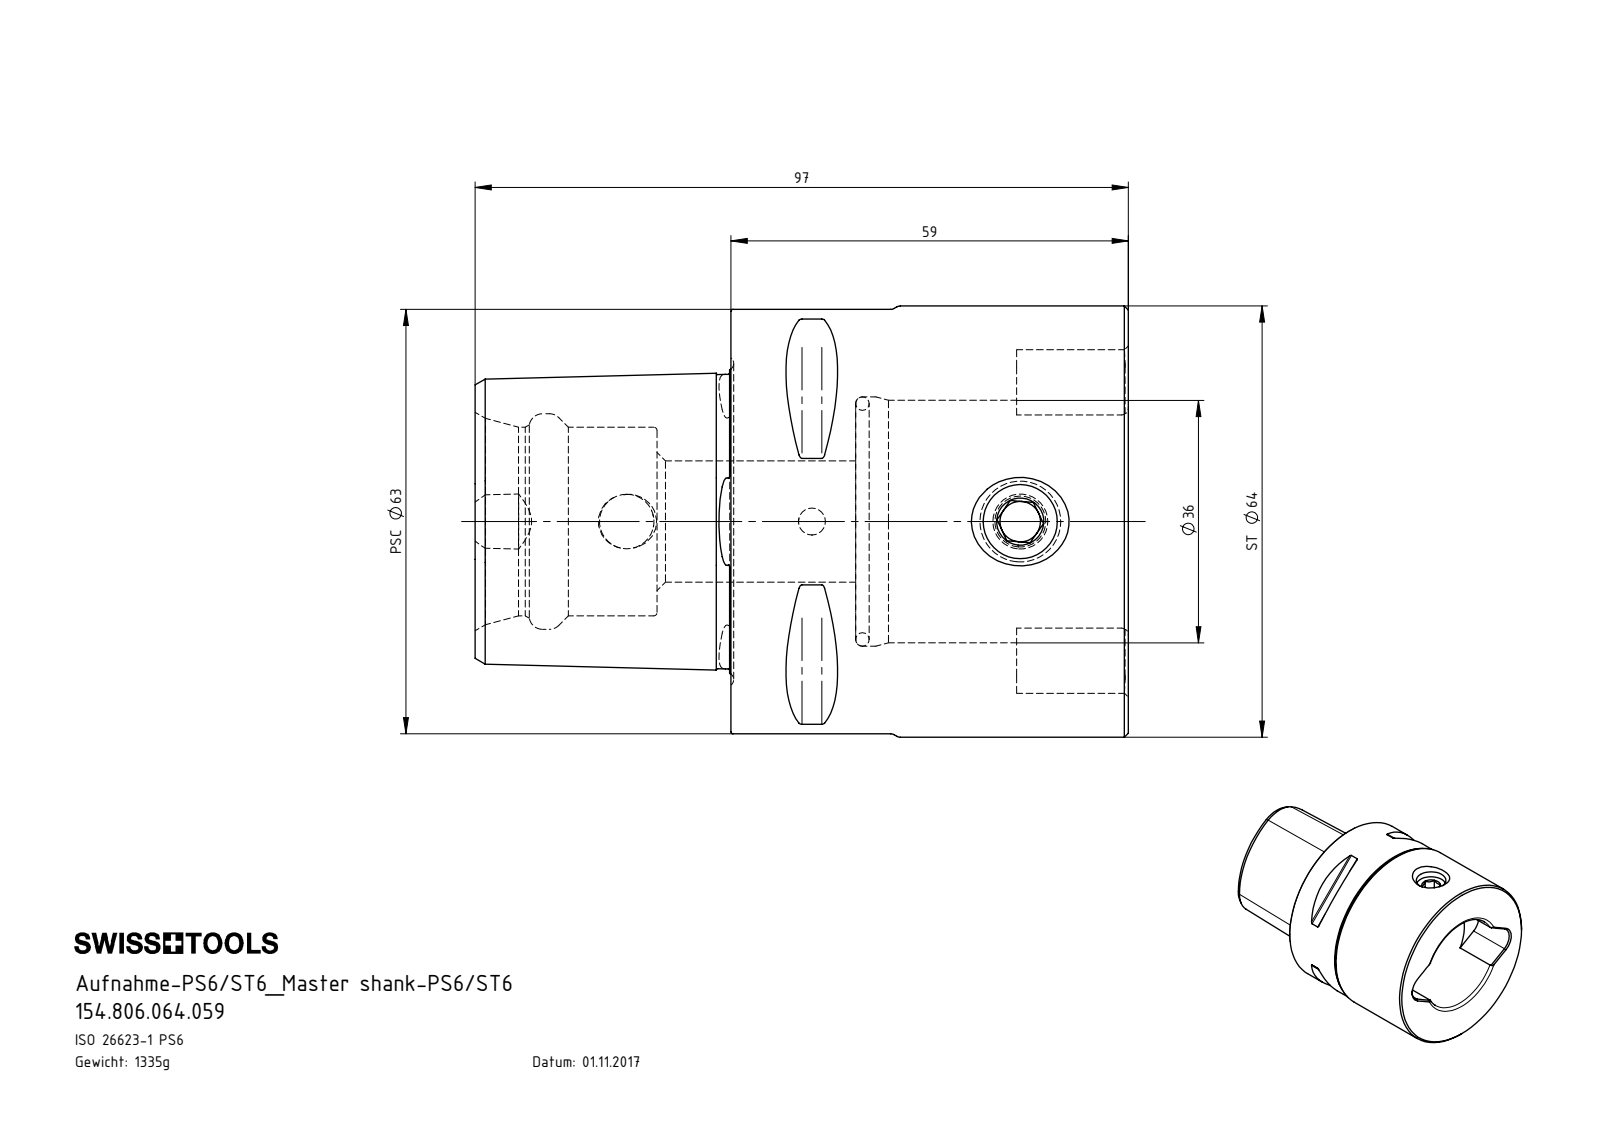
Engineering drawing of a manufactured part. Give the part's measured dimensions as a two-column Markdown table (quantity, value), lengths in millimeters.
| quantity | value |
| --- | --- |
| part name | PS6.ST6.K01.059; ST6-ER1.001.018_A; PS6-ST6.K01.059_B; DIN 3771 - 33x2 |
| STEP written by | SolidWorks 2017 (AUTOMOTIVE_DESIGN) |
| units | millimeters |
| bodies | 3 solids, 131 faces (42 planar, 25 cylindrical, 64 other) |
| overall size | 97 × 64 × 64 |
| volume | 170 389 mm³ |
| surface area | 33 894 mm² |
| round holes (diameter × count) | 4 × 1, 6 × 1, 8.1 × 1, 11 × 1, 18 × 1, 28 × 1, 32 × 1, 36 × 1, 37 × 1 |
| round bosses / shafts (diameter × count) | 64 × 1, 63 × 1, 12 × 1 |
| partial cylindrical surfaces (radius × count) | 0.5 × 8, 5.2 × 2, 6 × 1 |
| main face-to-face distances | 59, 18.5, 40.5, 38, 56.5, 97, 24.88, 30.7, 27, 11 |
| hole center spacings | 27.5, 30.95, 58.45 |
